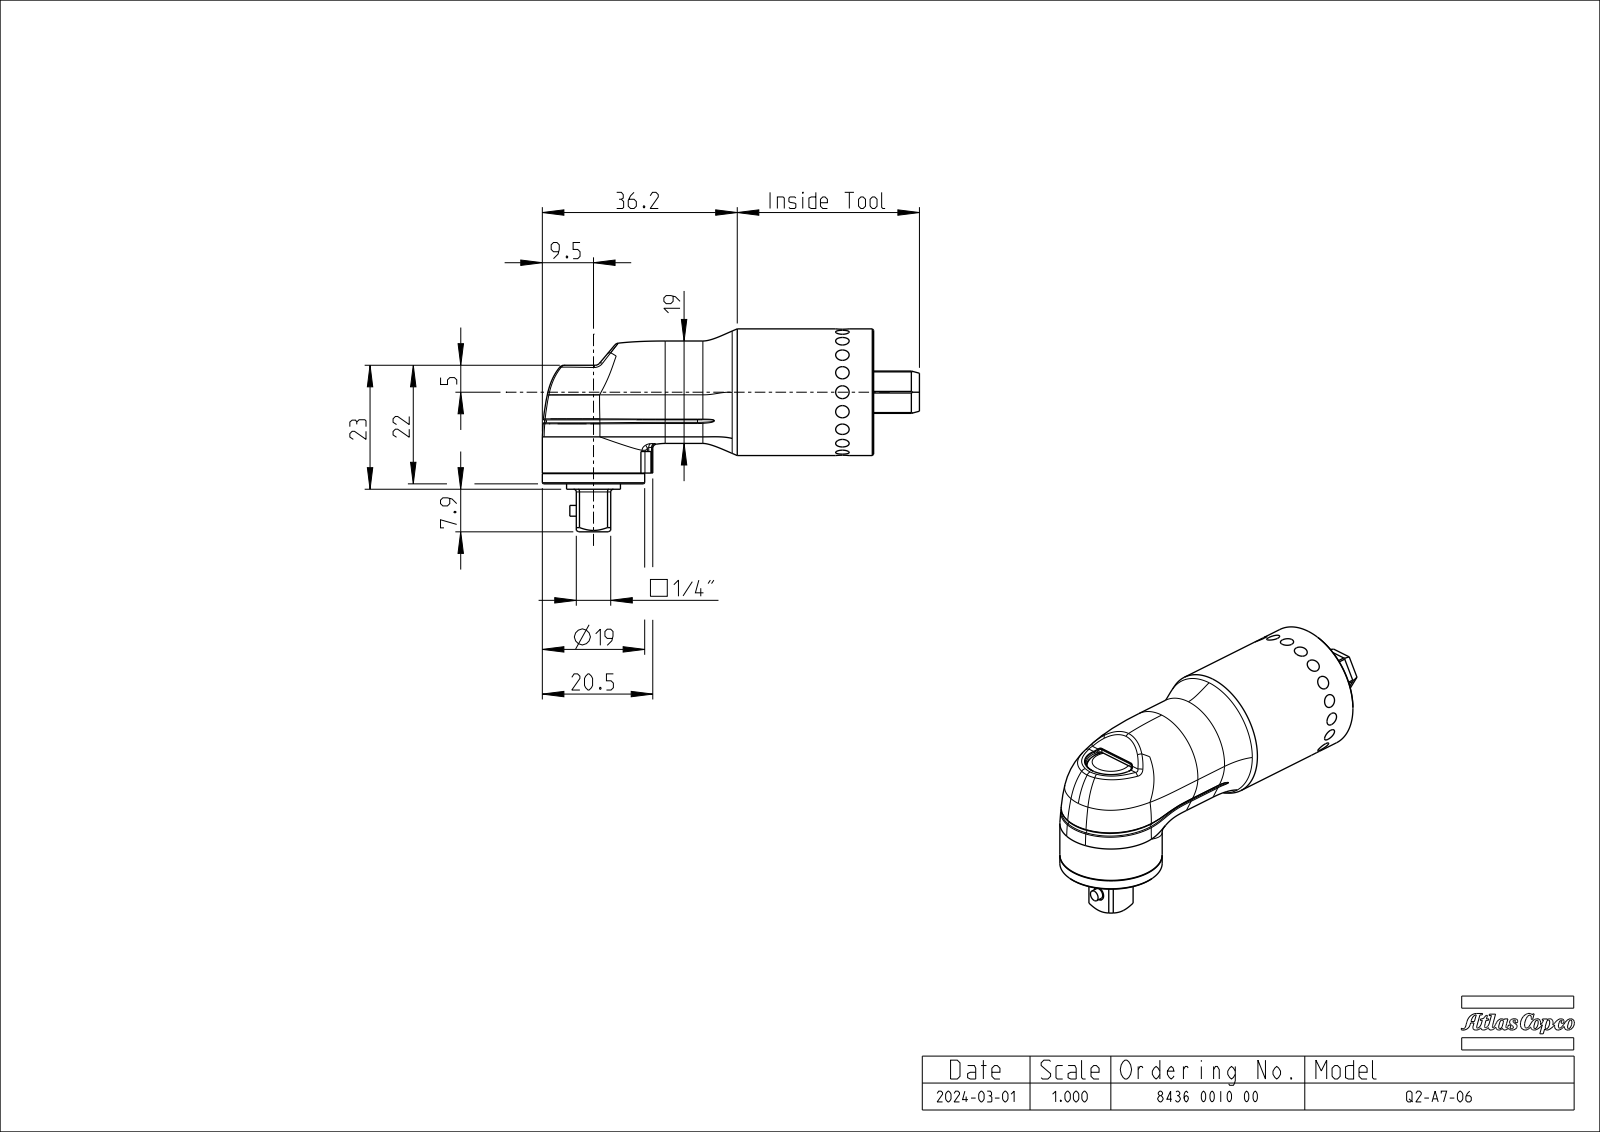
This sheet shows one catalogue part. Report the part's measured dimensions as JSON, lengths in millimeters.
{"part_name": "4211581980_NOIP", "step_written_by": "CREO PARAMETRIC BY PTC INC, 2022414 (CONFIG_CONTROL_DESIGN)", "units": "millimeters", "bodies": {"solids": 1, "faces": 221, "planar": 36, "cylindrical": 45, "other": 140}, "overall_size": [61.5, 37.65, 23.5], "volume_mm3": 23254, "surface_area_mm2": 5418, "round_holes": [[2.6, 4]], "round_bosses_or_shafts": [[23.5, 1], [19, 1], [10, 1], [2, 1]], "partial_cylinders_radius": [[0.5, 8], [0.3, 6], [0.2, 4], [0.75, 4], [0.4, 1], [1, 1], [9.5, 1], [11, 1]], "face_to_face_distances": [6.38, 21.9, 48.81, 55.19, 1, 22.9, 2.5, 1.5, 20.4, 7.9], "hole_center_spacings": [10.39, 14.7]}
